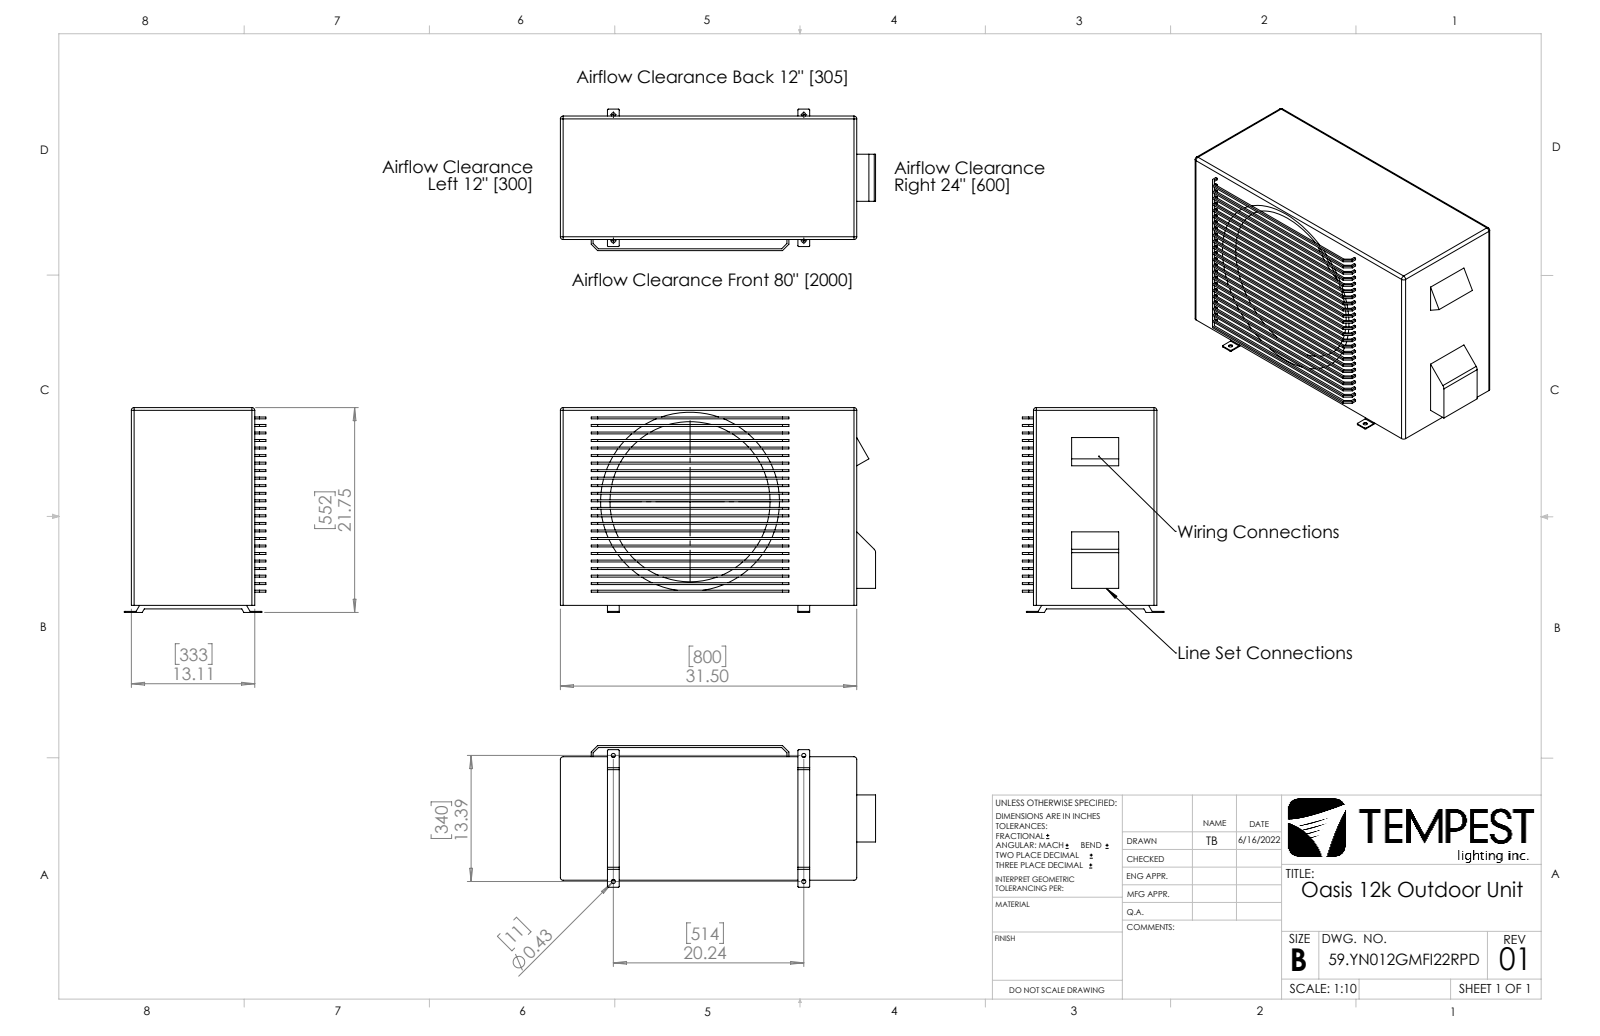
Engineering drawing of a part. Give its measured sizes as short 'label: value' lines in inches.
name: 59.ODU.12 R01; 59.ODU.LAB; Pioneer ODU Simple_Pioneer 12k ODU - YN012GMFI19RPD
written by: SolidWorks 2020 (AUTOMOTIVE_DESIGN)
unit: in
bodies: 2 solids, 1751 faces (1354 planar, 306 cylindrical, 91 other)
size: 34.975 × 22 × 14.5
volume: 3 547 in³; area: 5 022 in²
holes: 2× ⌀0.875, 1× ⌀0.835, 1× ⌀17
bosses: 1× ⌀4
rounds: 104× R0.25, 47× R0.1, 18× R0.107, 12× R0.75, 10× R0.05, 9× R1, 8× R0.233, 8× R0.685
face distances: 1.5, 1.25, 20, 12.025, 10.525, 0.2, 2.875, 9.15, 7.65, 0.1
hole spacings: 1.5
